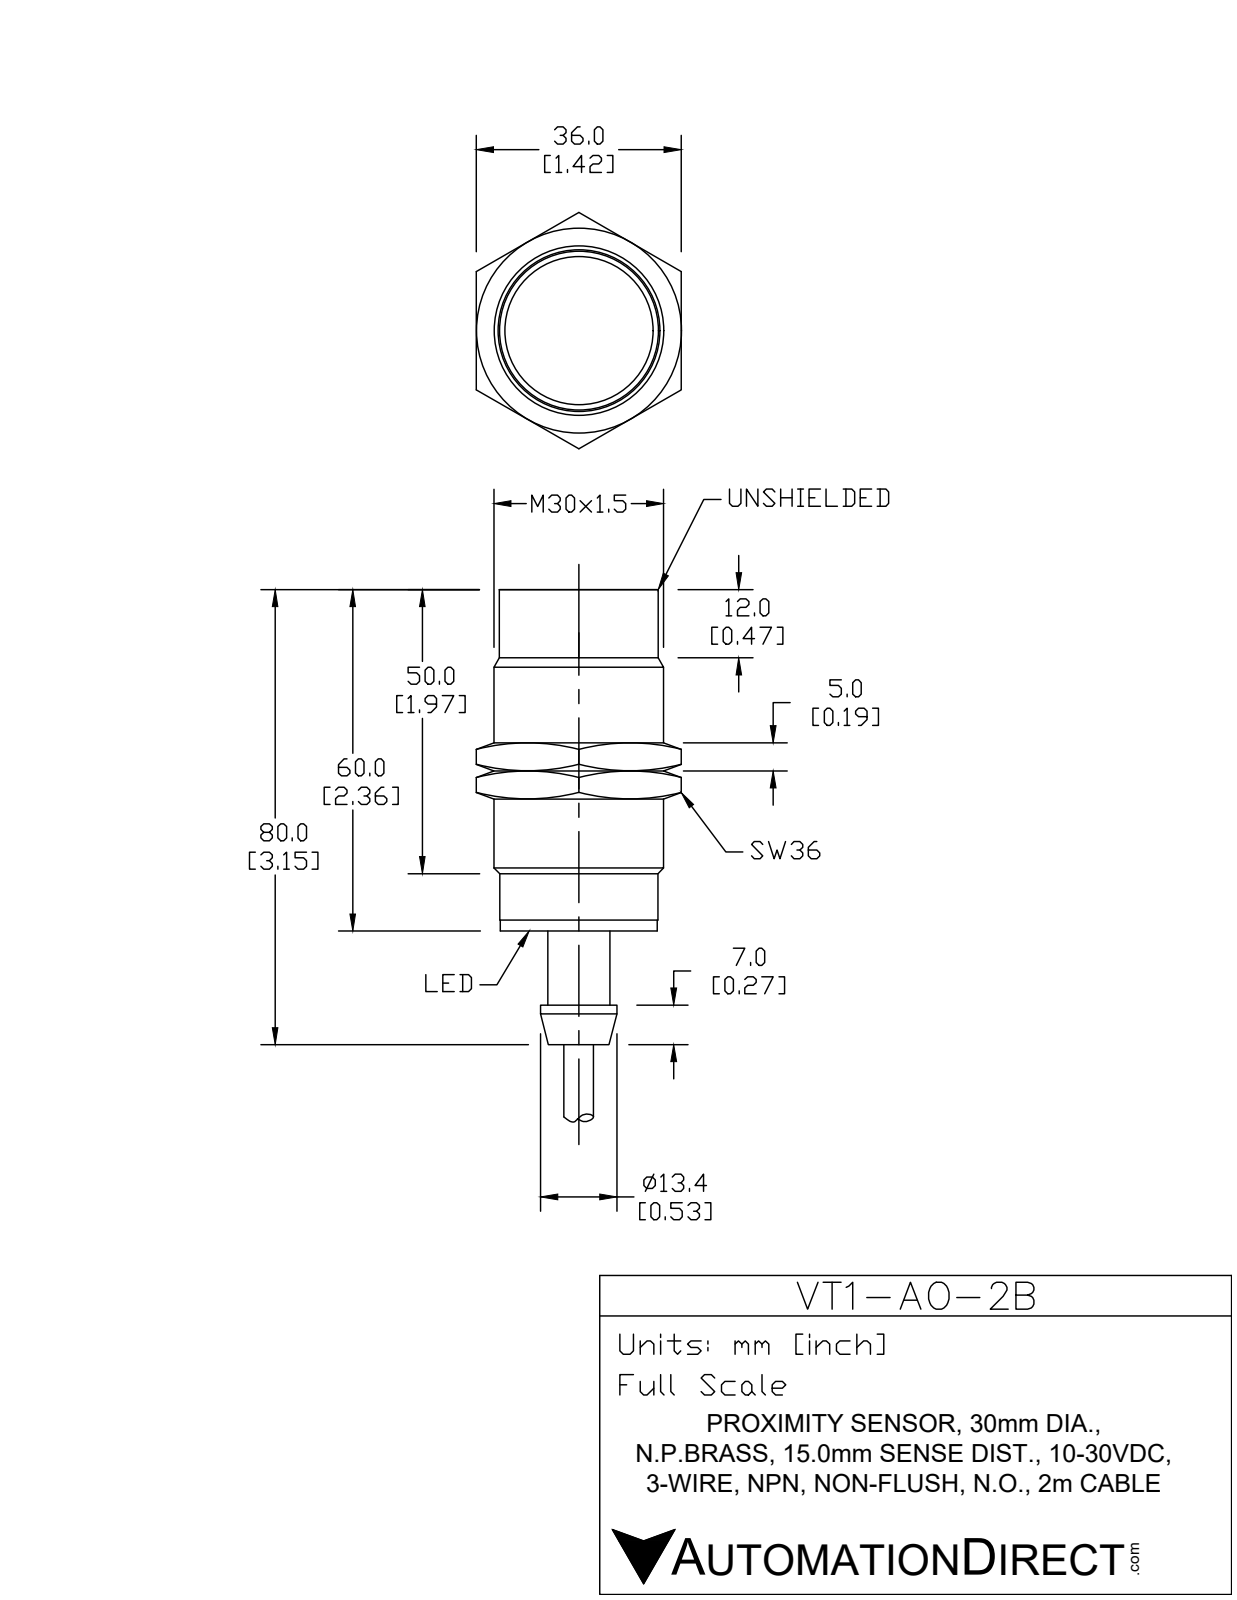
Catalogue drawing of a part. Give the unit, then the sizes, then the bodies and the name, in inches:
Units: inches
Overall size (bounding box): 3.858 × 1.181 × 1.181
Round holes (diameter × count): ⌀0.224 ×1
Round bosses / shafts (diameter × count): ⌀1.181 ×1, ⌀1.094 ×1, ⌀0.531 ×1, ⌀0.433 ×1, ⌀0.217 ×1
Main face-to-face distances: 1.811, 0.472, 2.283, 2.362, 1.89, 0.079, 3.15, 2.677, 0.866, 0.787
Volume: 2.554 in³ · Surface area: 16.83 in²
Bodies: 4 solids, 38 faces (10 planar, 14 cylindrical, 14 other)
Part name (STEP PRODUCT): VT1-A0-2B
STEP written by: SolidWorks 2017 (AUTOMOTIVE_DESIGN)
